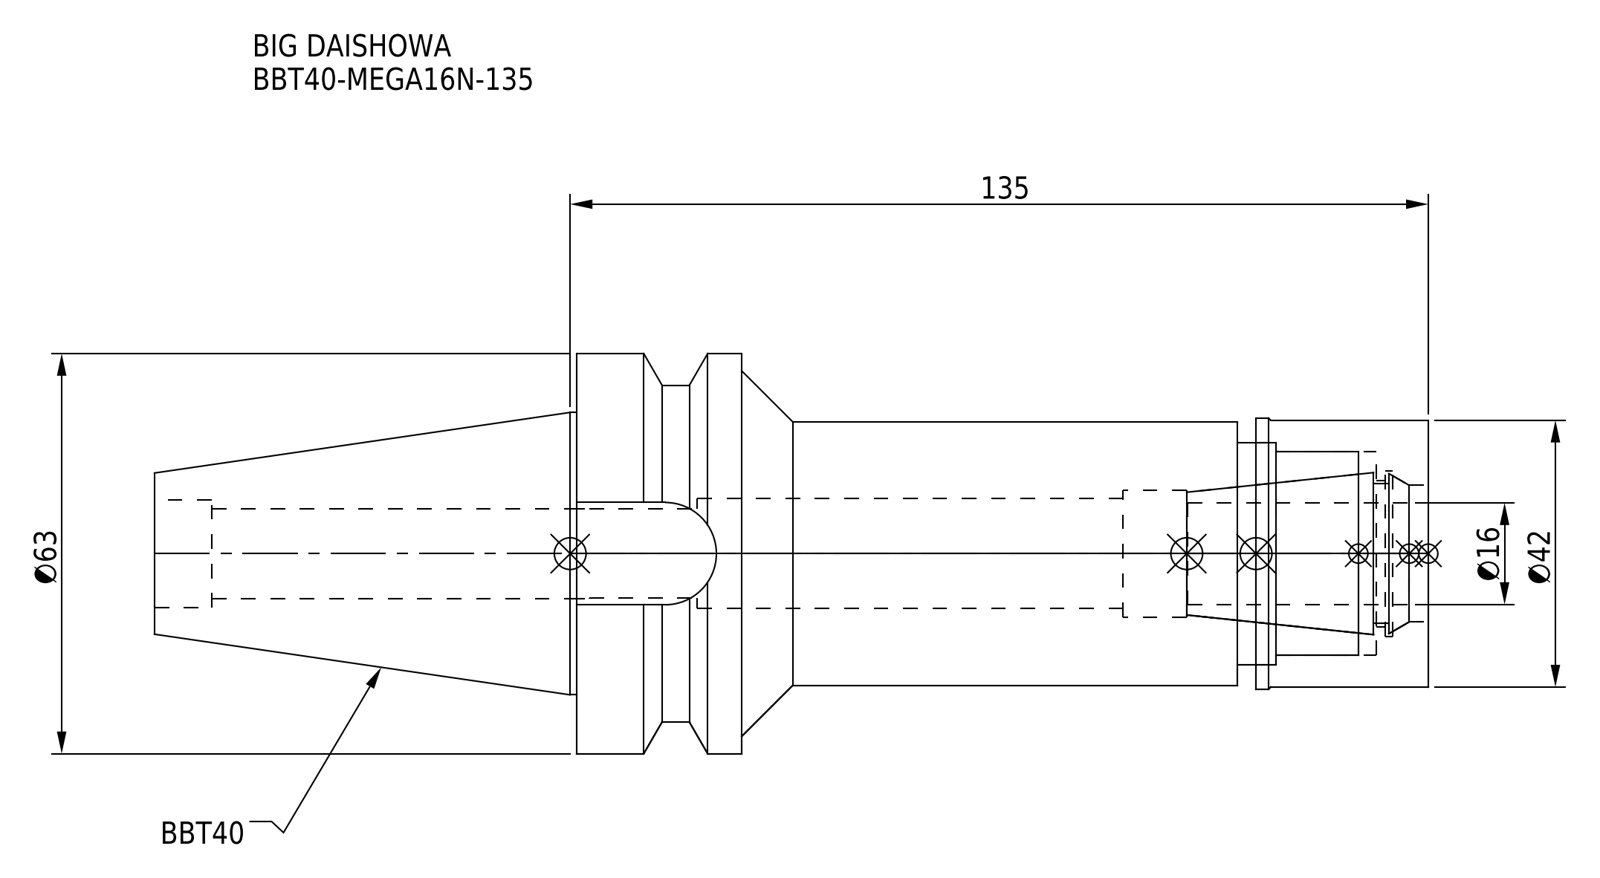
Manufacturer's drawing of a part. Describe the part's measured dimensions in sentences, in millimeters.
The part is named "BBT40-MEGA16N-135-160.stp; BBT40-MEGA16N-135_1.stp; BBT40-MEGA16N-135; BBT40MN16135-160_ASM.stp (+3 more)". Its 3-D file was written by "SolidWorks 2019 (CONFIG_CONTROL_DESIGN)". It is 2 solids with 80 faces: 24 planar, 42 cylindrical and 14 other. Overall it measures 200.4 by 63 by 63 millimeters. Its volume is 237 125 cubic millimeters and its surface area 48 353 square millimeters. Round holes: 1 of diameter 14, 1 of diameter 14.1, 1 of diameter 14.2, 1 of diameter 17, 1 of diameter 17.3, 1 of diameter 20, 1 of diameter 21.5, 1 of diameter 23, 1 of diameter 26, 1 of diameter 32, 1 of diameter 35. Round bosses or shafts: 1 of diameter 63, 1 of diameter 53, 1 of diameter 44.45, 1 of diameter 42.7, 1 of diameter 42, 1 of diameter 41.5. Partial cylindrical surfaces (rounded edges, fillets, slot ends): 1 of radius 8.05. The main face-to-face distances are 134, 108, 26, 16.1, 27.1, 80.9, 106.9, 24, 3, 30.1.
